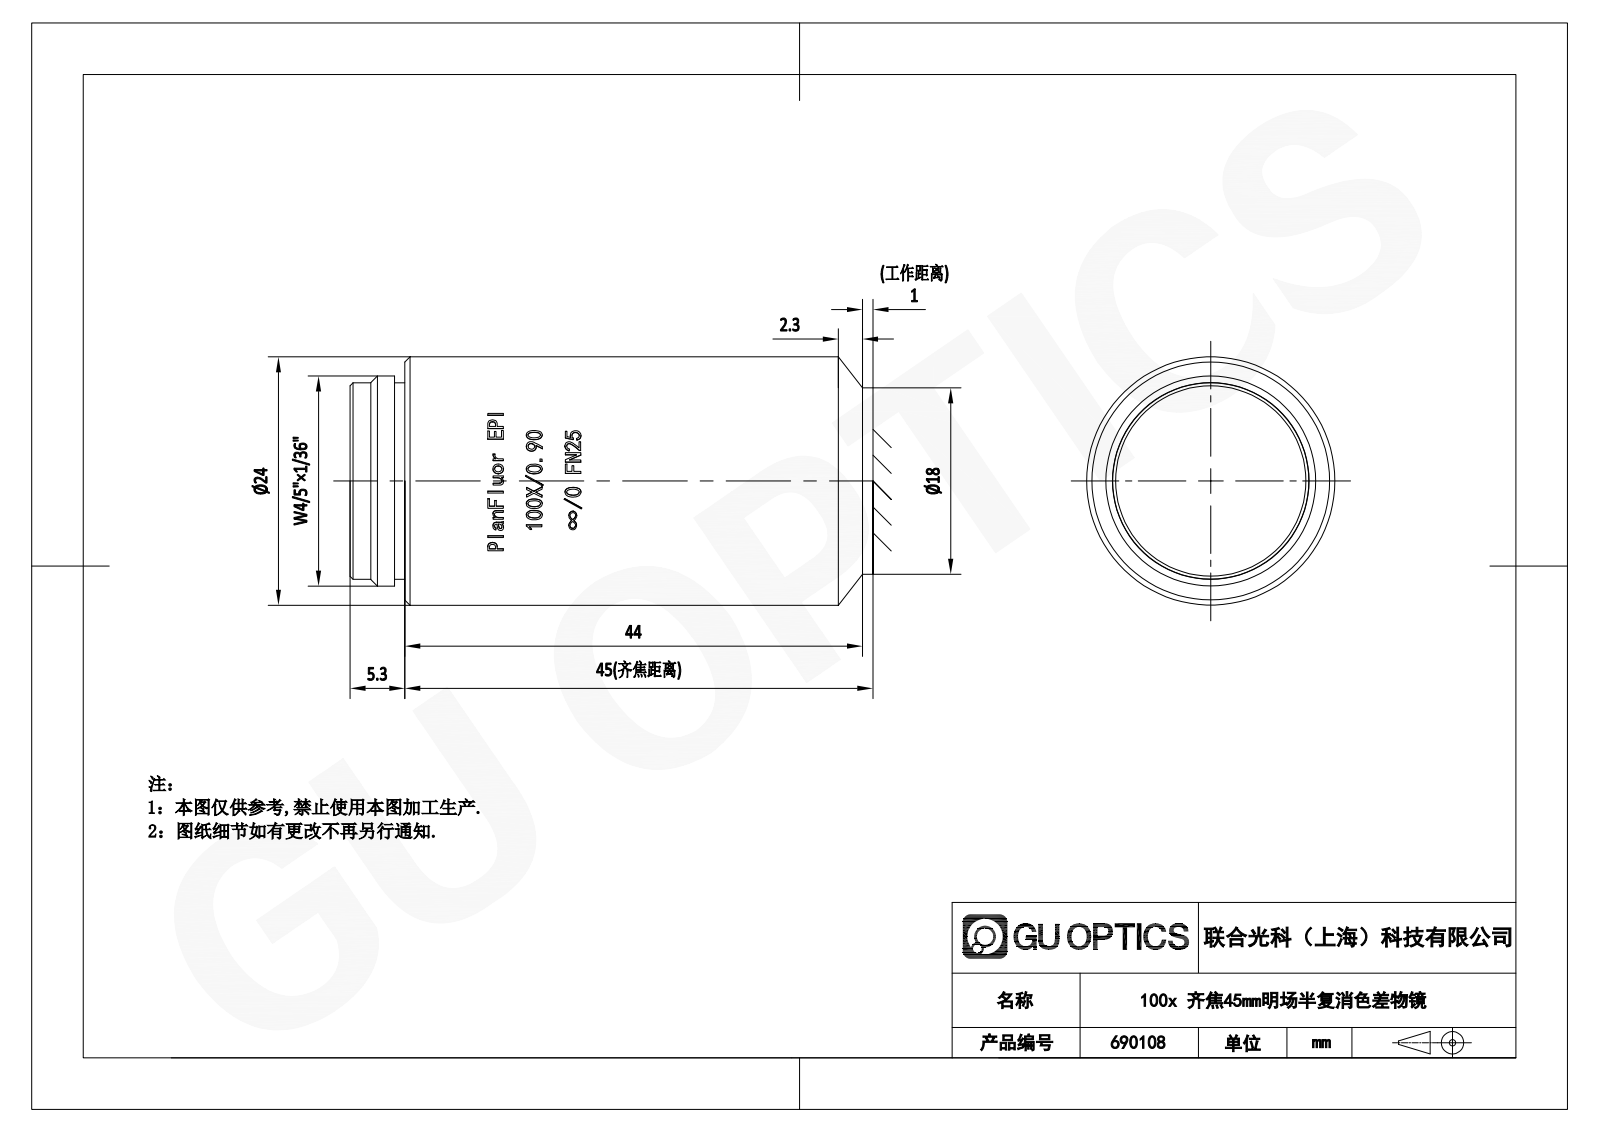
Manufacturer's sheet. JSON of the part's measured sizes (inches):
{"part_name": "690108", "step_written_by": "SolidWorks 2020 (CONFIG_CONTROL_DESIGN)", "units": "inches", "bodies": {"solids": 1, "faces": 300, "planar": 126, "cylindrical": 48, "other": 126}, "overall_size": [1.951, 0.947, 0.945], "volume_in3": 1.303, "surface_area_in2": 6.935, "round_bosses_or_shafts": [[0.945, 1], [0.8, 1], [0.748, 1]], "partial_cylinders_radius": [[0.474, 1]], "face_to_face_distances": [1.951, 0.209, 1.742, 0.169, 0.039, 1.781, 0.079, 0.091, 0.13, 1.872]}
